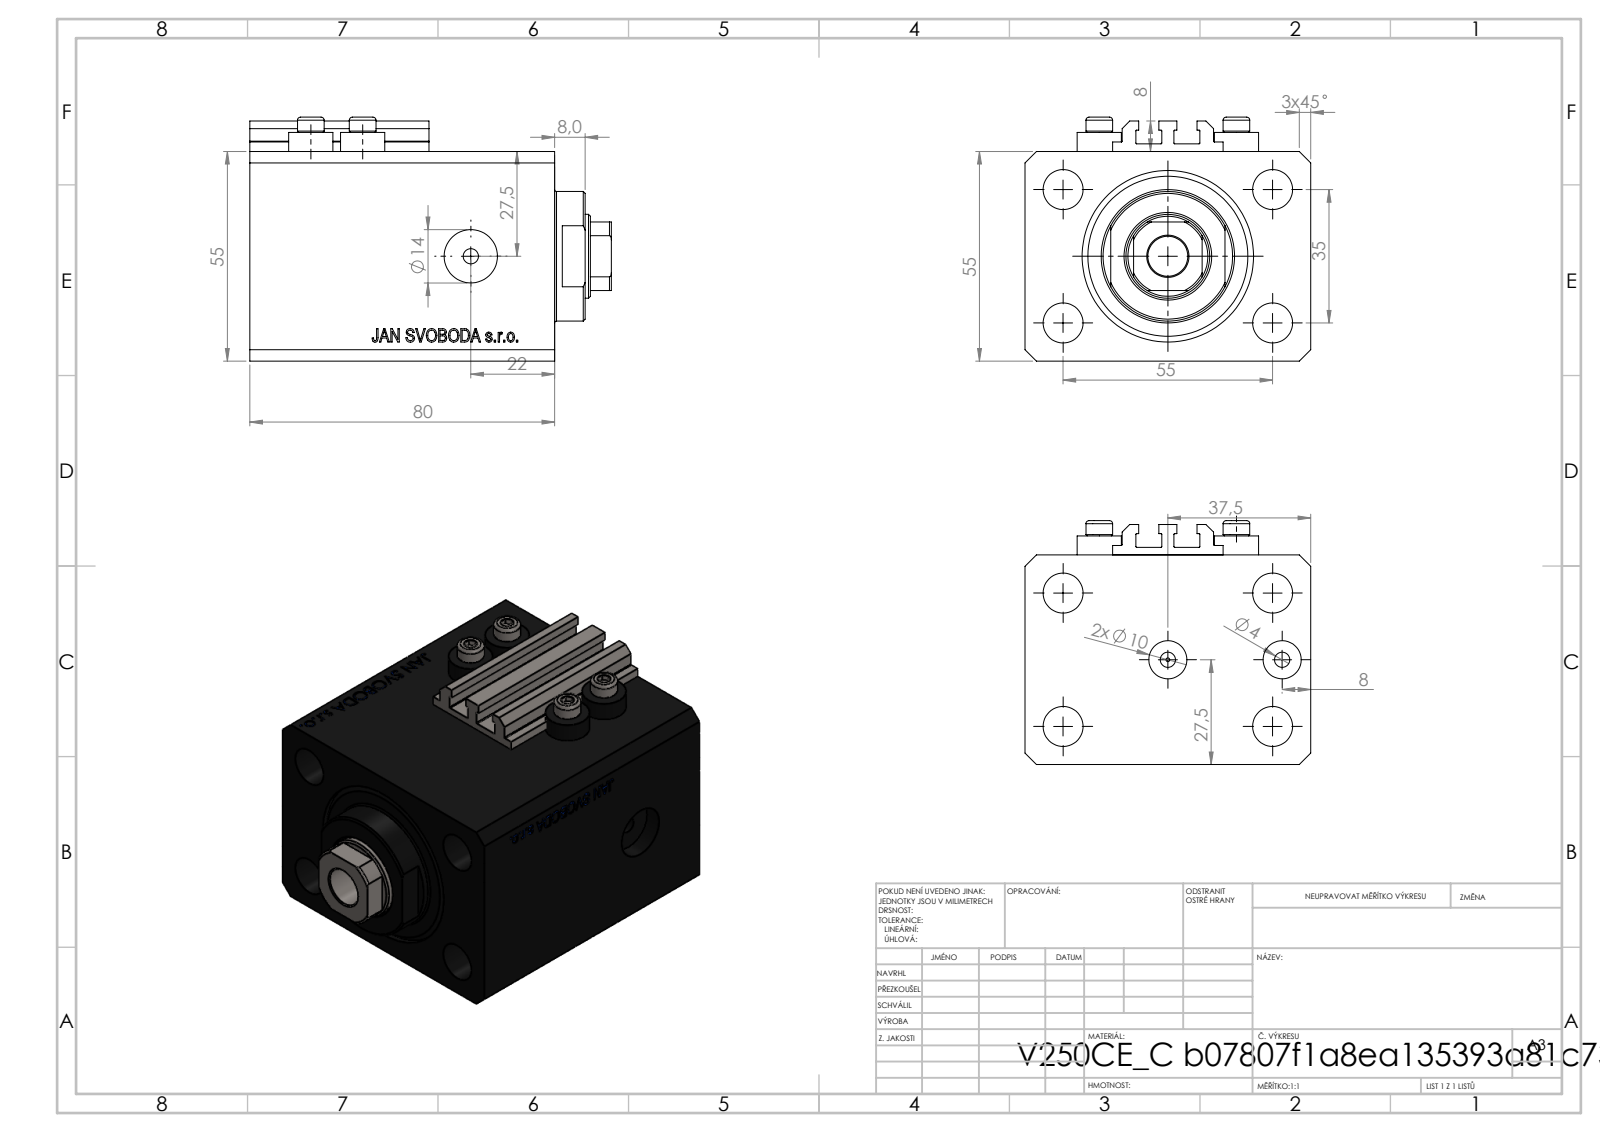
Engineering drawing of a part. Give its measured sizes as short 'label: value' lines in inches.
name: V250CE_C_VCP; ALLEN BOLT V250CE; V250CE_VC_C; V250CE_C_Body
written by: SolidWorks 2019 (CONFIG_CONTROL_DESIGN)
unit: in
bodies: 8 solids, 1042 faces (504 planar, 92 cylindrical, 446 other)
size: 3.736 × 2.953 × 2.52
volume: 18.59 in³; area: 115.4 in²
holes: 8× ⌀0.157, 5× ⌀0.413, 2× ⌀0.394, 2× ⌀0.551, 1× ⌀0.049, 1× ⌀0.866, 1× ⌀1.26, 1× ⌀1.772
bosses: 4× ⌀0.457, 4× ⌀0.276, 1× ⌀1.339
rounds: 10× R0.008, 1× R0.413
face distances: 2.165, 2.953, 3.15, 1.067, 2.083, 1.693, 0.39, 2.76, 0.118, 0.315
hole spacings: 1.283, 1.417, 0.535, 0.696, 1.378, 1.515, 2.165, 2.366
